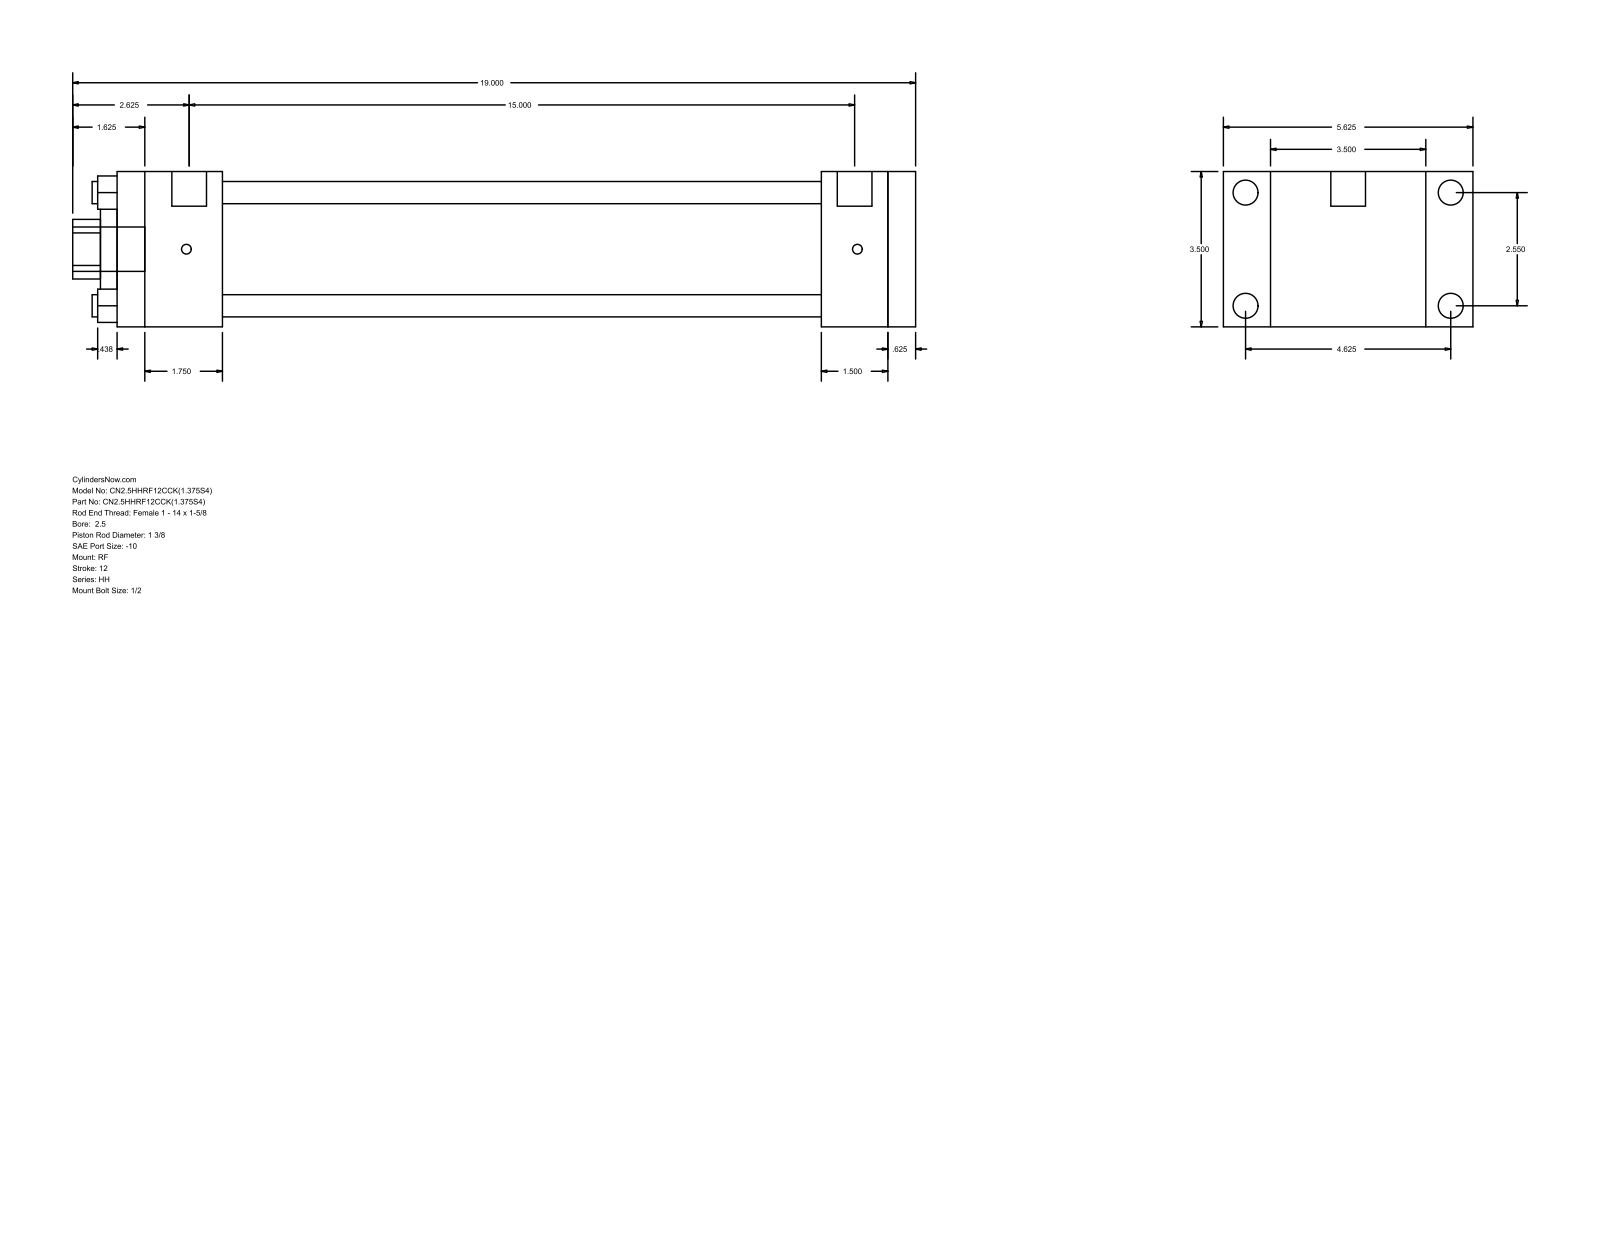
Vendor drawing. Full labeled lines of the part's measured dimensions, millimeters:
Part name (STEP PRODUCT): HH_RF__0250_1.375
STEP written by: GSSL Pune (CONFIG_CONTROL_DESIGN)
Units: millimetres
Bodies: 0 solids, 92 faces (64 planar, 28 cylindrical, 0 other)
Overall size (bounding box): 482.6 × 142.88 × 88.9
Round holes (diameter × count): ⌀12.7 ×4, ⌀34.92 ×1, ⌀50.8 ×1, ⌀73.03 ×1
Round bosses / shafts (diameter × count): ⌀14.3 ×4, ⌀5.56 ×4, ⌀19.84 ×2, ⌀25.4 ×1
Partial cylindrical surfaces — rounded edges, fillets, slot ends (radius × count): R17.06 ×1
Main face-to-face distances: 88.9, 15.87, 441.33, 457.2, 60.32, 381.01, 396.88, 403.22, 342.9, 38.11
Hole centre spacings: 45.79, 64.76, 91.58
